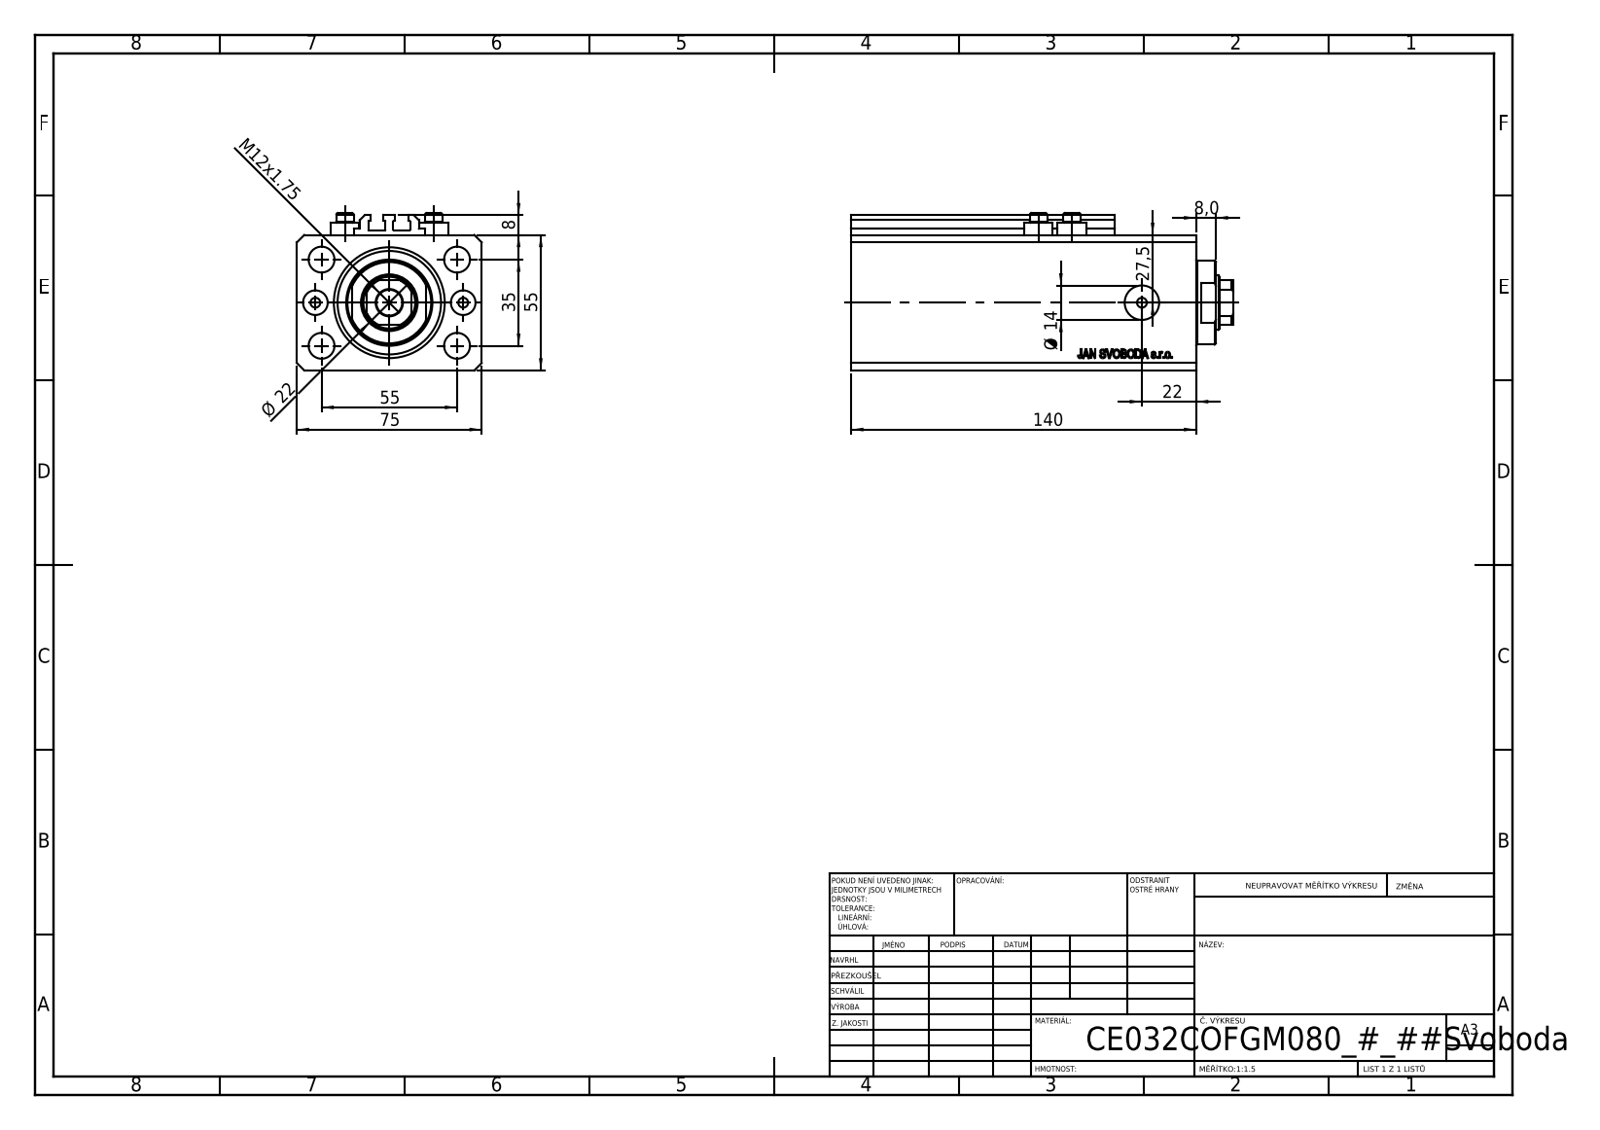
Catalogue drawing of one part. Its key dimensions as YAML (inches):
part_name: "ALLEN BOLT V250CE; V250CE_C_Body; V250CE_VC_C; V250CE_C_VCP"
step_written_by: "SolidWorks 2019 (CONFIG_CONTROL_DESIGN)"
units: inches
bodies: {solids: 8, faces: 1034, planar: 504, cylindrical: 86, other: 444}
overall_size: [6.102, 2.953, 2.52]
volume: 31.29
surface_area: 171.7
round_holes:
  - {diameter: 0.157, count: 8}
  - {diameter: 0.413, count: 5}
  - {diameter: 0.394, count: 2}
  - {diameter: 0.551, count: 2}
  - {diameter: 0.866, count: 1}
  - {diameter: 1.26, count: 1}
  - {diameter: 1.772, count: 1}
round_bosses_or_shafts:
  - {diameter: 0.457, count: 4}
  - {diameter: 0.276, count: 4}
  - {diameter: 1.339, count: 1}
partial_cylinders:
  - {radius: 0.008, count: 10}
  - {radius: 0.413, count: 1}
face_to_face_distances: [2.165, 2.953, 5.512, 0.591, 4.921, 0.39, 4.531, 5.122, 0.098, 0.079]
hole_center_spacings: [0.696, 1.283, 2.366, 0.535, 1.181, 1.378, 1.417, 1.515]
